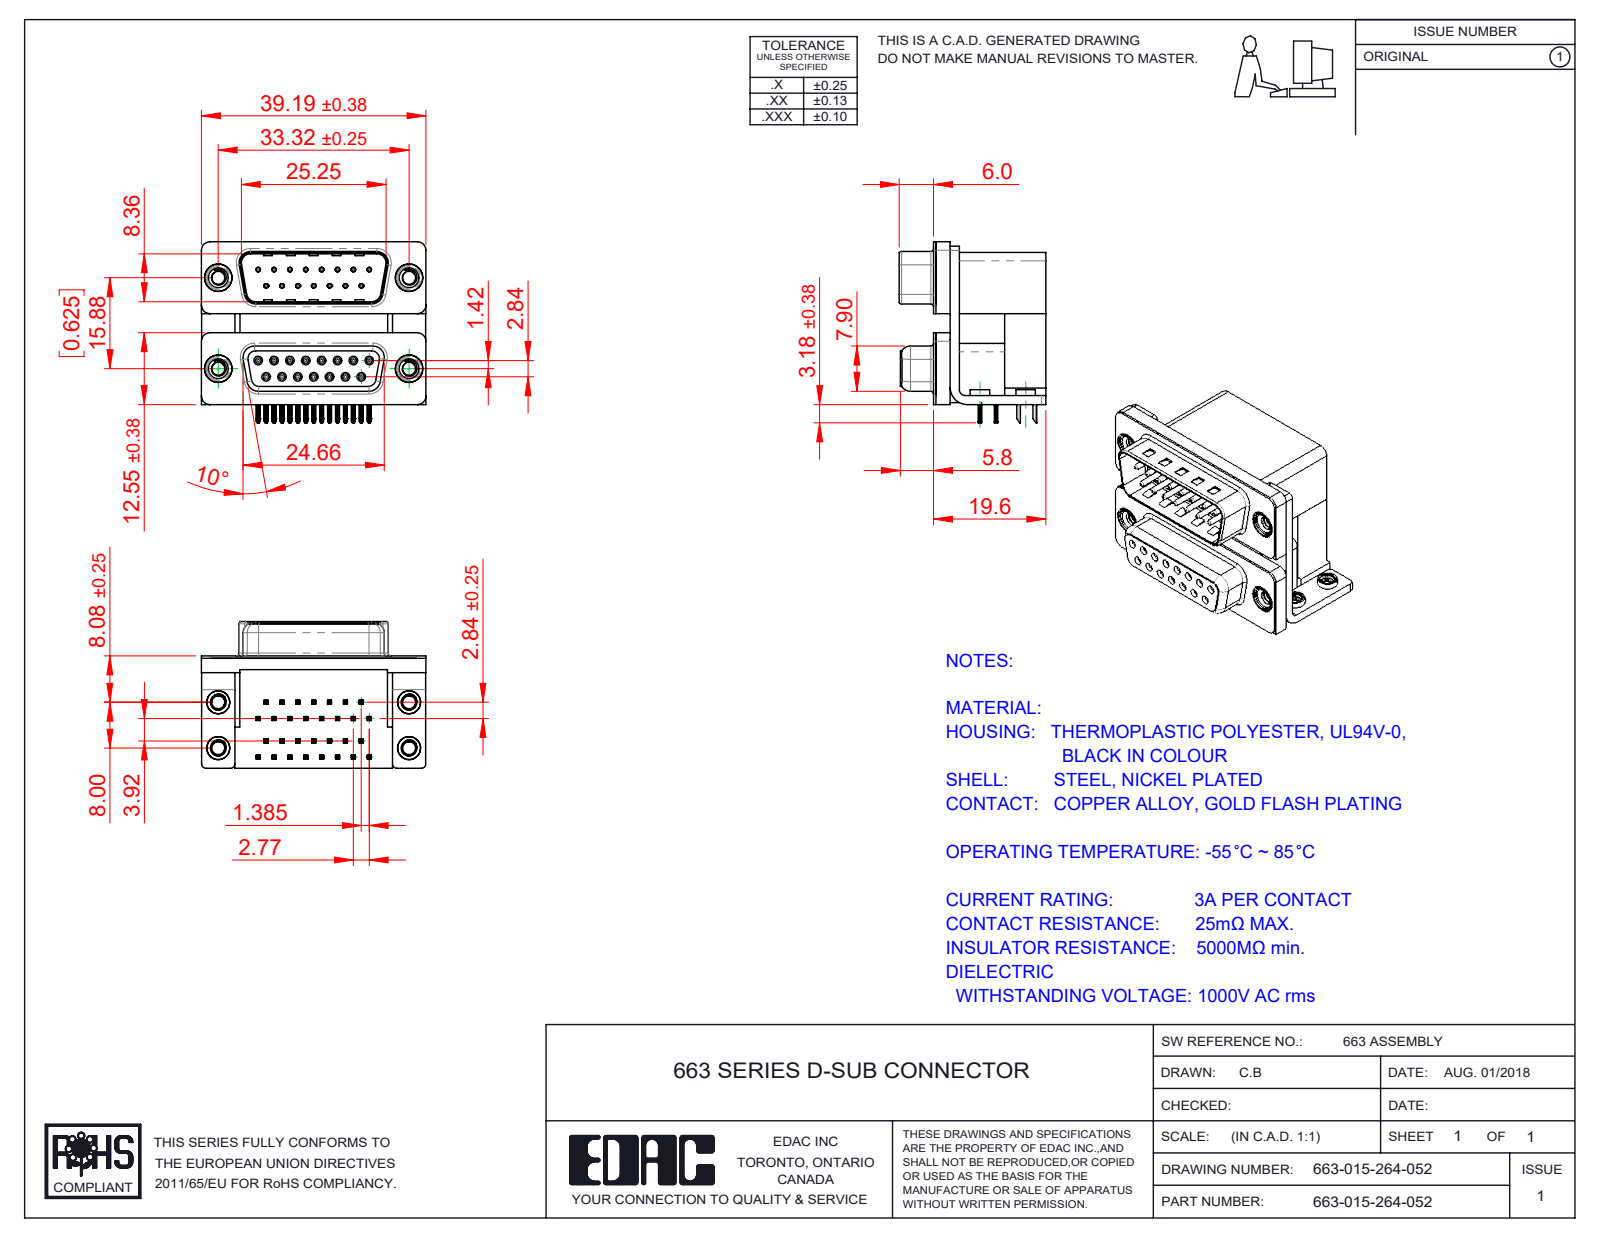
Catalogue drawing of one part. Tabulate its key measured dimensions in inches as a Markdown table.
| quantity | value |
| --- | --- |
| part name | 663 Threaded Rivet_4-40; 663 4-40 Threaded Board Mount; 663 Housing Spacer_15 Contacts L; 663 Contact Bottom Upper_L (+8 more) |
| STEP written by | SolidWorks 2020 (CONFIG_CONTROL_DESIGN) |
| units | inches |
| bodies | 45 solids, 4052 faces (2027 planar, 1090 cylindrical, 935 other) |
| overall size | 1.543 × 1.244 × 1.008 |
| volume | 0.893 in³ |
| surface area | 25.44 in² |
| round holes (diameter × count) | 0.031 × 30, 0.014 × 15, 0.035 × 15, 0.089 × 8, 0.108 × 4, 0.126 × 4, 0.138 × 4, 0.157 × 4, 0.189 × 4, 0.197 × 4 |
| round bosses / shafts (diameter × count) | 0.047 × 15, 0.03 × 15, 0.193 × 4, 0.187 × 4, 0.157 × 4, 0.154 × 4, 0.134 × 4 |
| partial cylindrical surfaces (radius × count) | 0.004 × 120, 0.006 × 60, 0.01 × 60, 0.005 × 30, 0.014 × 30, 0.059 × 16, 0.013 × 15, 0.02 × 12 |
| main face-to-face distances | 0.016, 0.756, 0.657, 0.098, 0.421, 0.283, 0.472, 0.374, 0.114, 0.772 |
| hole center spacings | 0.124, 0.635, 0.109, 0.662, 0.218, 0.327, 0.625, 0.706 |
